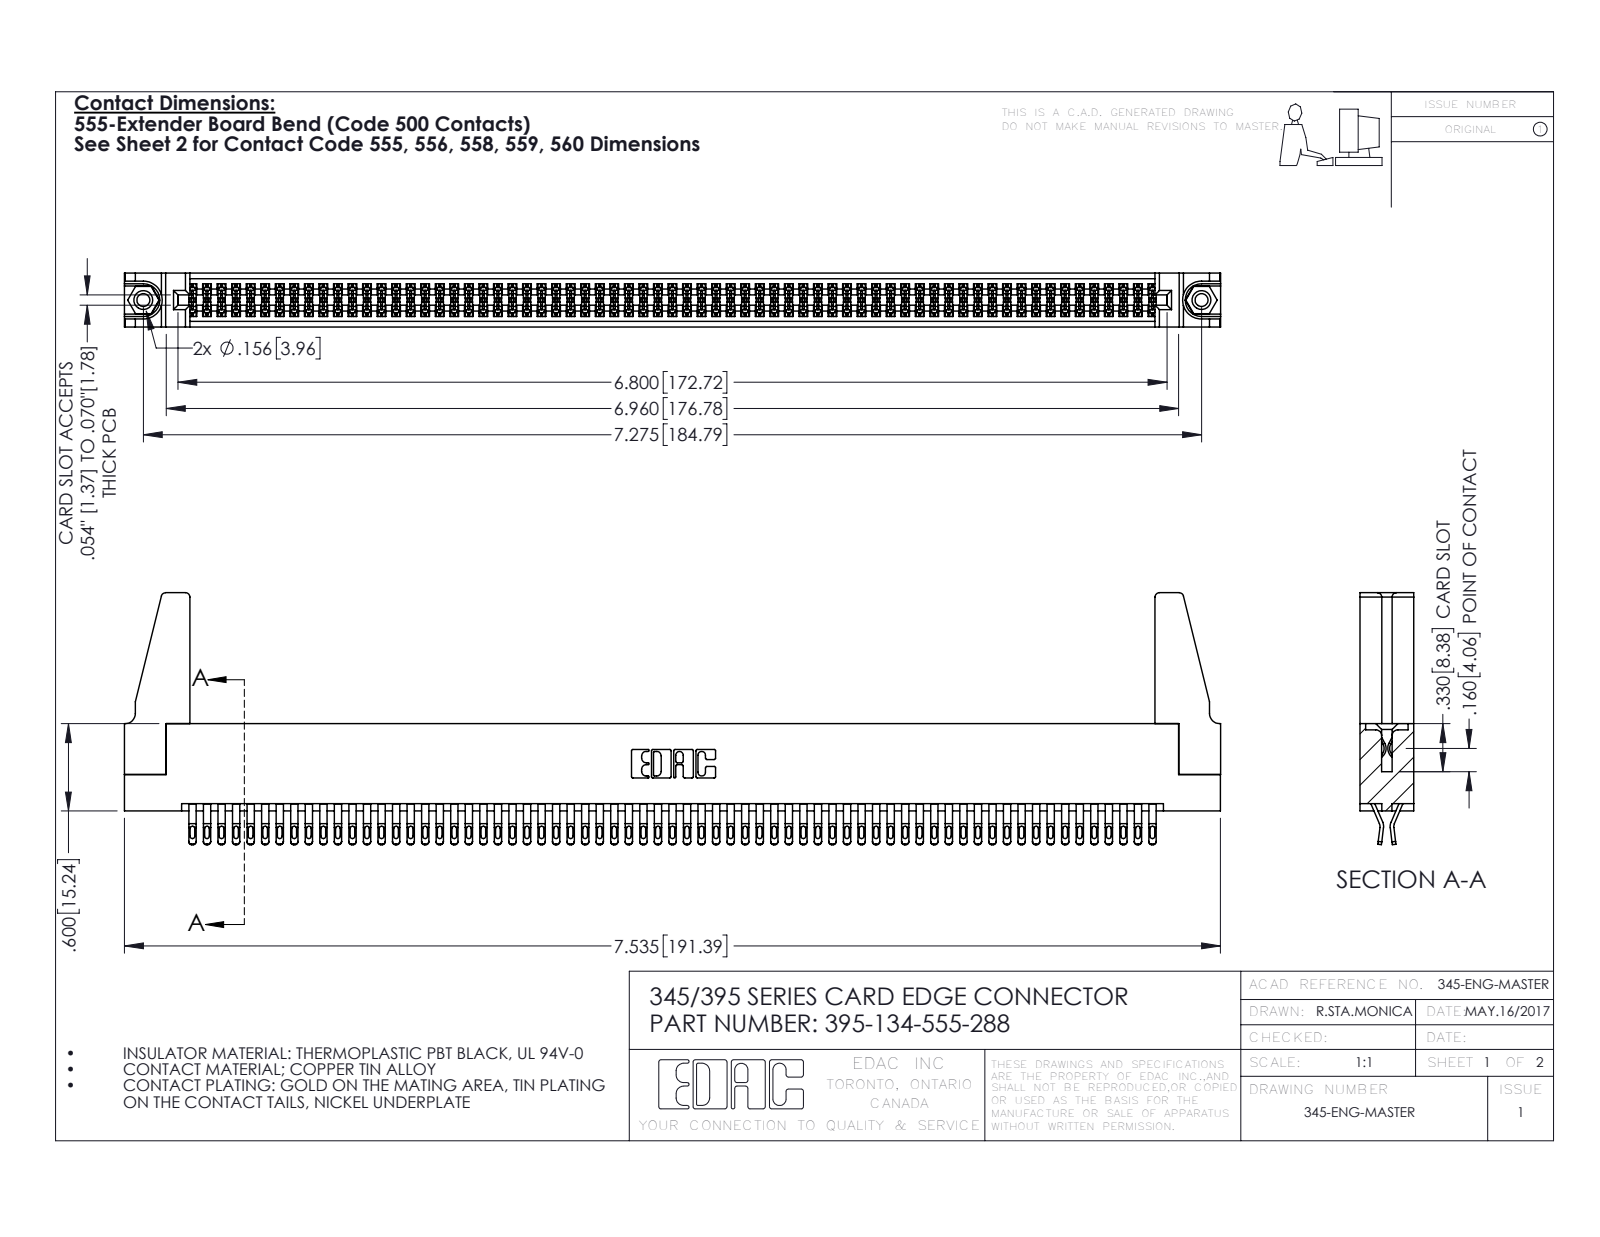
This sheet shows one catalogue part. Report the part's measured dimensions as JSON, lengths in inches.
{"part_name": "345-220-078_345-220-088; 395-134-555-288; 345-250-001_345-250-001-102; 345-292-001_555 Tail (+1 more)", "step_written_by": "SolidWorks 2016 (CONFIG_CONTROL_DESIGN)", "units": "inches", "bodies": {"solids": 139, "faces": 7754, "planar": 4306, "cylindrical": 3432, "other": 16}, "overall_size": [7.536, 1.732, 0.37], "volume_in3": 1.371, "surface_area_in2": 51.71, "round_holes": [[0.089, 2], [0.125, 2], [0.156, 2], [0.064, 1]], "round_bosses_or_shafts": [[0.155, 2]], "partial_cylinders_radius": [[0.016, 335], [0.02, 268], [0.006, 201], [0.01, 22], [0.03, 8], [0.007, 6], [0.031, 6], [0.026, 3]], "face_to_face_distances": [0.072, 0.298, 0.37, 0.025, 0.2, 0.098, 0.272, 0.225, 0.175, 0.149], "hole_center_spacings": [0.27, 7.039, 7.275]}
